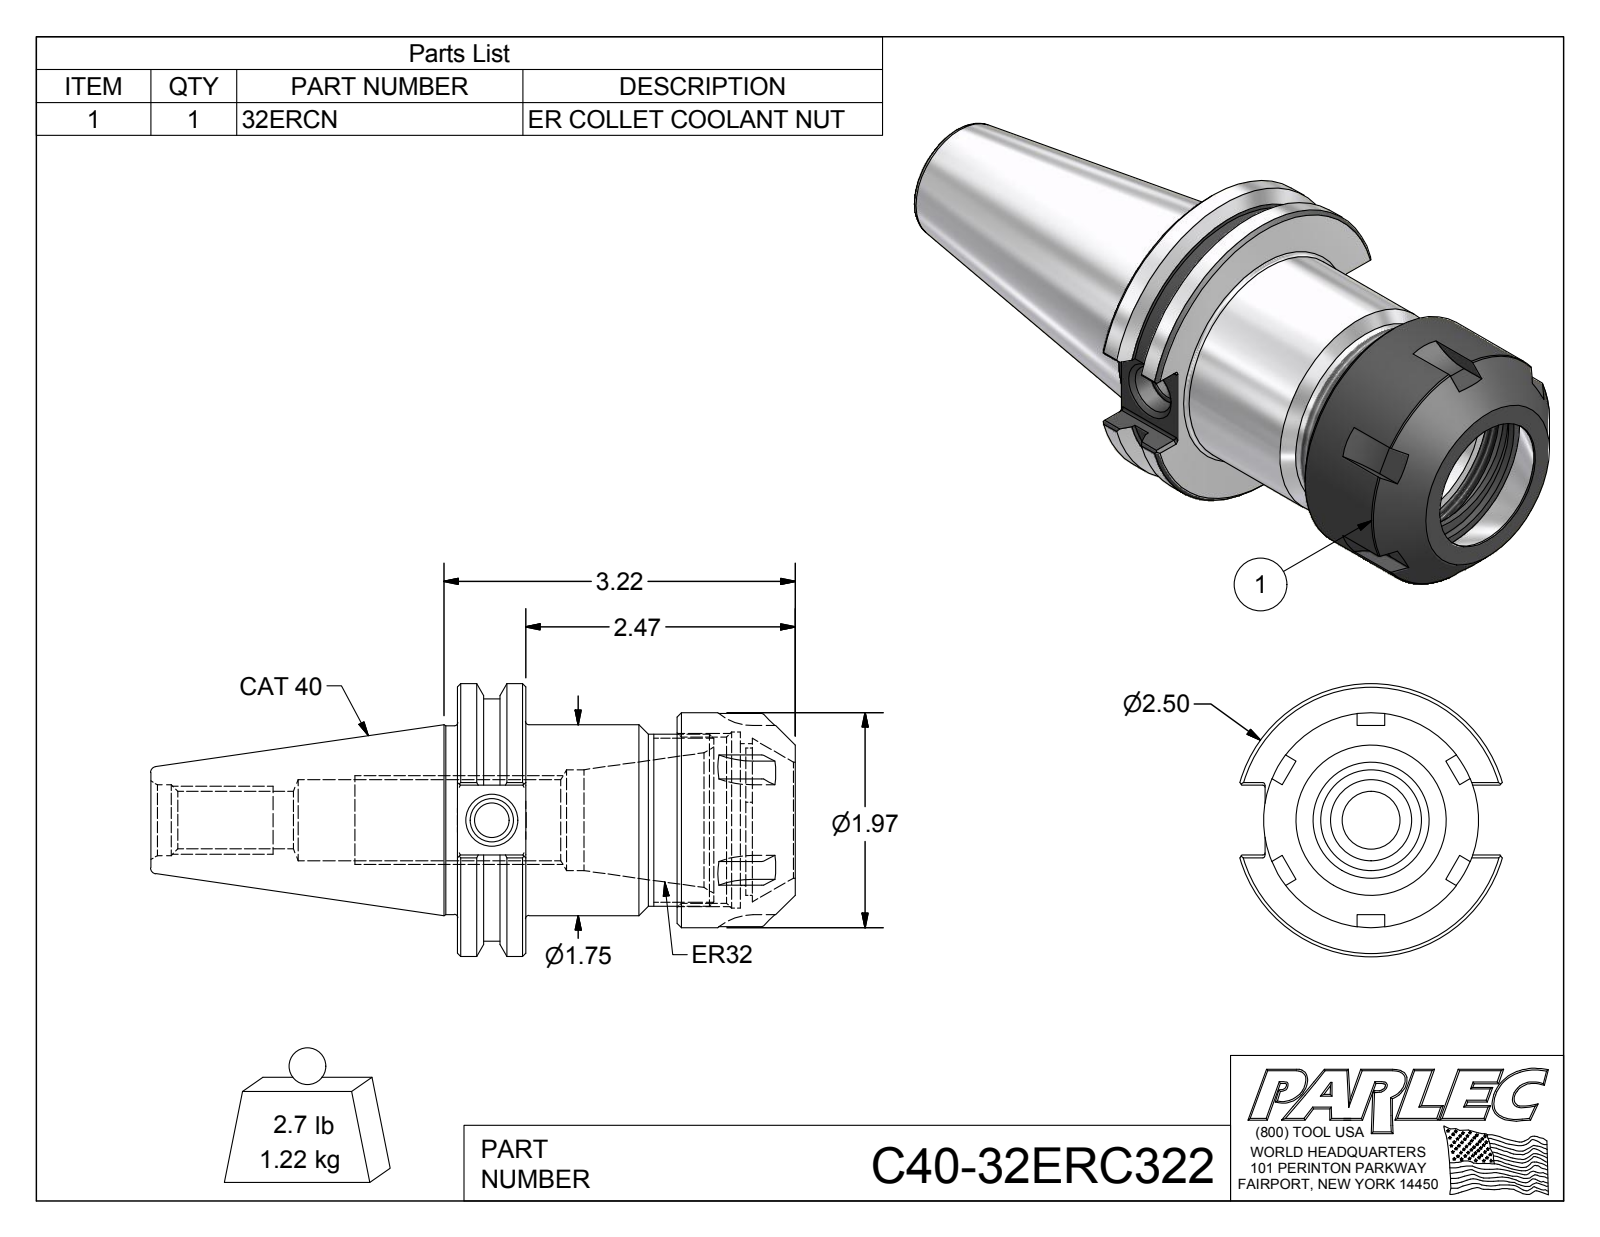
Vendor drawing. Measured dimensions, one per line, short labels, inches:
name: C40-32ERC322; C40-32ER3-1; 32ERCN
written by: Autodesk Inventor 2012 (AUTOMOTIVE_DESIGN)
unit: in
bodies: 2 solids, 127 faces (54 planar, 39 cylindrical, 34 other)
size: 5.908 × 2.5 × 2.403
volume: 9.347 in³; area: 61.44 in²
holes: 1× ⌀0.315, 1× ⌀0.399, 1× ⌀0.527, 1× ⌀0.648, 1× ⌀0.745, 1× ⌀0.925, 1× ⌀1.063, 1× ⌀1.299, 1× ⌀1.522, 1× ⌀1.614
bosses: 1× ⌀2.5, 1× ⌀2.219, 1× ⌀1.969, 1× ⌀1.75, 1× ⌀1.73, 1× ⌀1.575
rounds: 12× R0.02, 6× R0.5, 1× R0.689
face distances: 0.625, 2.012, 1.387, 2.591, 1.966, 0.579, 3.095, 2.47, 1.083, 0.504
hole spacings: 0.059
